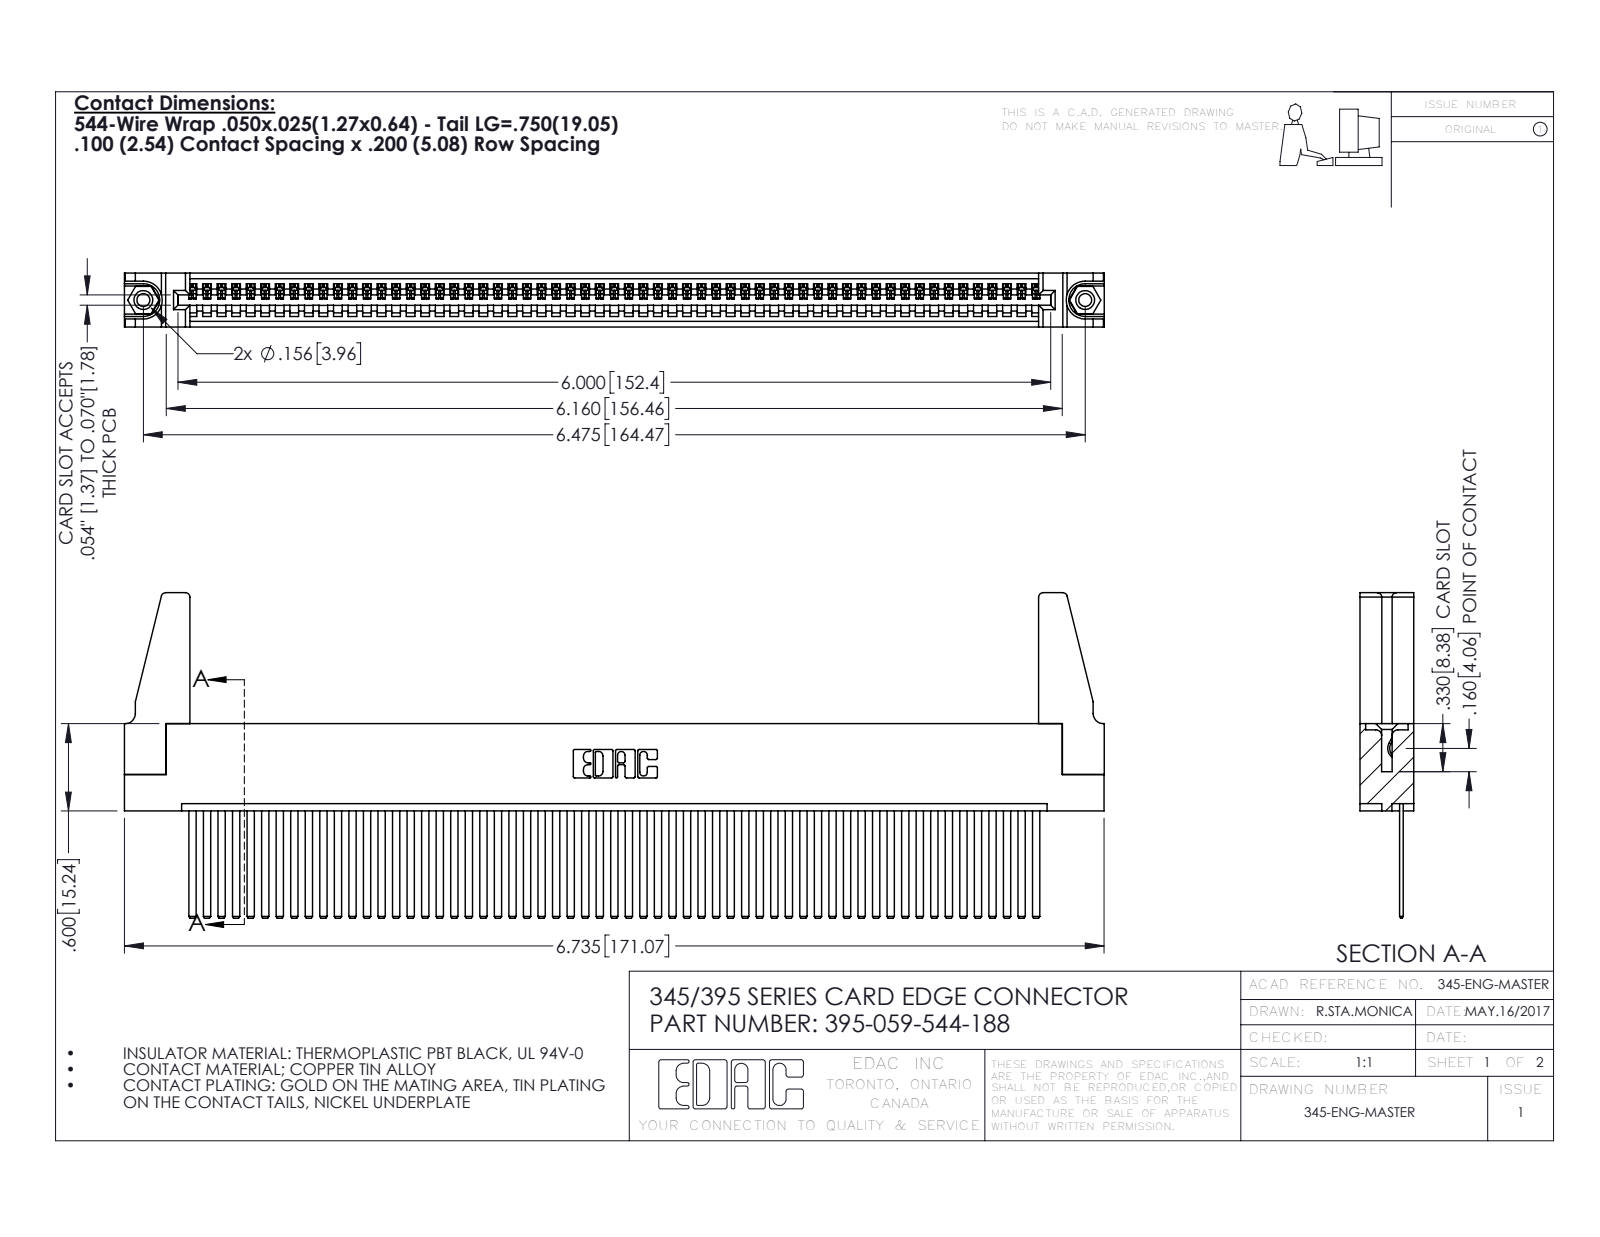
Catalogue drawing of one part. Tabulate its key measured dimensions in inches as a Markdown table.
| quantity | value |
| --- | --- |
| part name | 345 Part_Flush Mounting Lugs - 0.156 Dia-TH; 345-220-078_345-220-088; 395-059-544-188; 345-250-001_345-250-001-102 (+1 more) |
| STEP written by | SolidWorks 2016 (CONFIG_CONTROL_DESIGN) |
| units | inches |
| bodies | 64 solids, 3318 faces (2276 planar, 1026 cylindrical, 16 other) |
| overall size | 6.736 × 2.237 × 0.37 |
| volume | 1.24 in³ |
| surface area | 43.56 in² |
| round holes (diameter × count) | 0.089 × 2, 0.125 × 2, 0.156 × 2, 0.064 × 1 |
| round bosses / shafts (diameter × count) | 0.155 × 2 |
| partial cylindrical surfaces (radius × count) | 0.006 × 118, 0.01 × 22, 0.03 × 8, 0.007 × 6, 0.031 × 6, 0.026 × 3, 0.031 × 2, 0.04 × 2 |
| main face-to-face distances | 0.072, 0.298, 0.098, 0.272, 0.025, 0.37, 0.2, 0.225, 0.149, 0.072 |
| hole center spacings | 0.27, 6.239, 6.475 |
